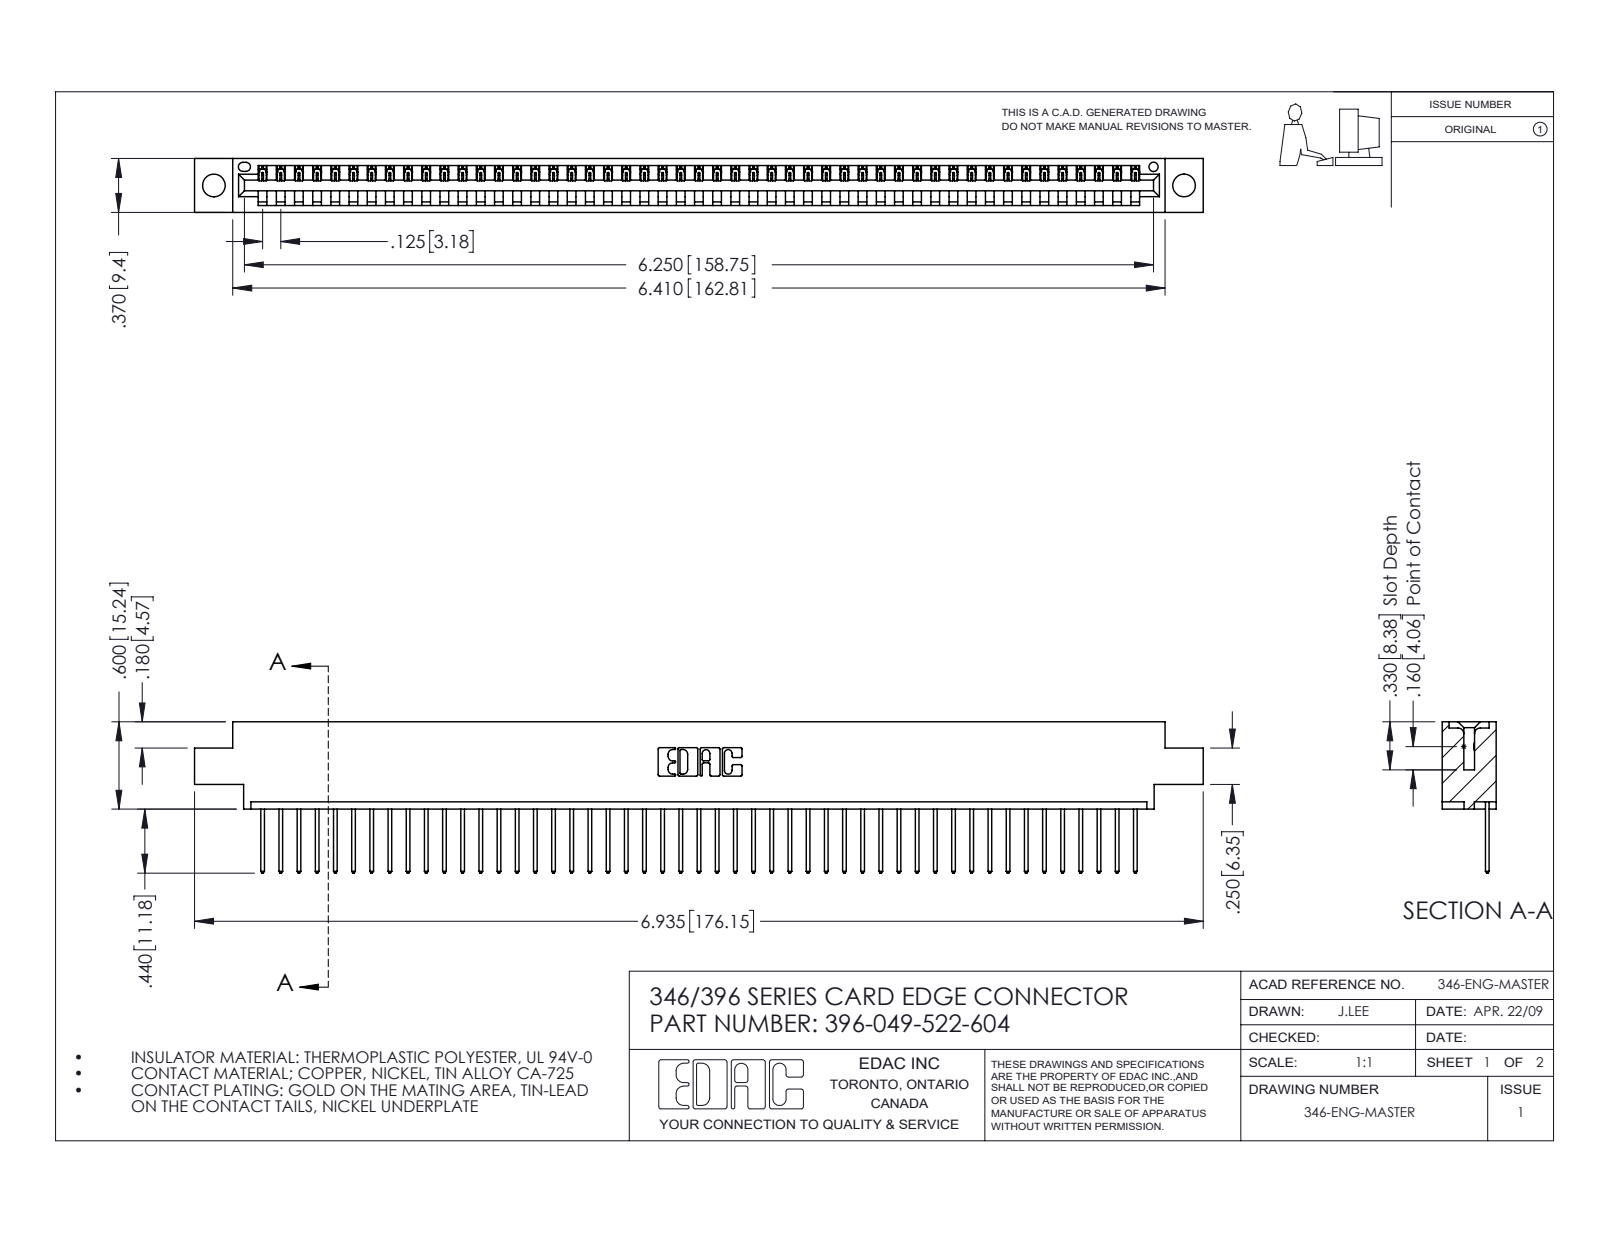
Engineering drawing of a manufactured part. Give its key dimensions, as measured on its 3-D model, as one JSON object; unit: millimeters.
{"part_name": "345-292-001_345-293-122; 396-049-522-604; 346 Part_0.170 Offset - 0.156 Dia-TH", "step_written_by": "SolidWorks 2016 (CONFIG_CONTROL_DESIGN)", "units": "millimeters", "bodies": {"solids": 50, "faces": 2968, "planar": 2040, "cylindrical": 928, "other": 0}, "overall_size": [176.1, 26.4, 9.4], "volume_mm3": 16670, "surface_area_mm2": 21060, "round_holes": [[4, 2], [1.6, 1]], "partial_cylinders_radius": [[0.2, 98], [0.3, 98], [0.3, 22], [0.2, 6], [0.8, 6], [0.7, 3], [0.8, 2], [1, 2]], "face_to_face_distances": [1.2, 8.2, 9.4, 6.4, 1.8, 7.6, 0.6, 3.8, 5.6, 2.5], "hole_center_spacings": [6.2, 164.1, 169.4]}
